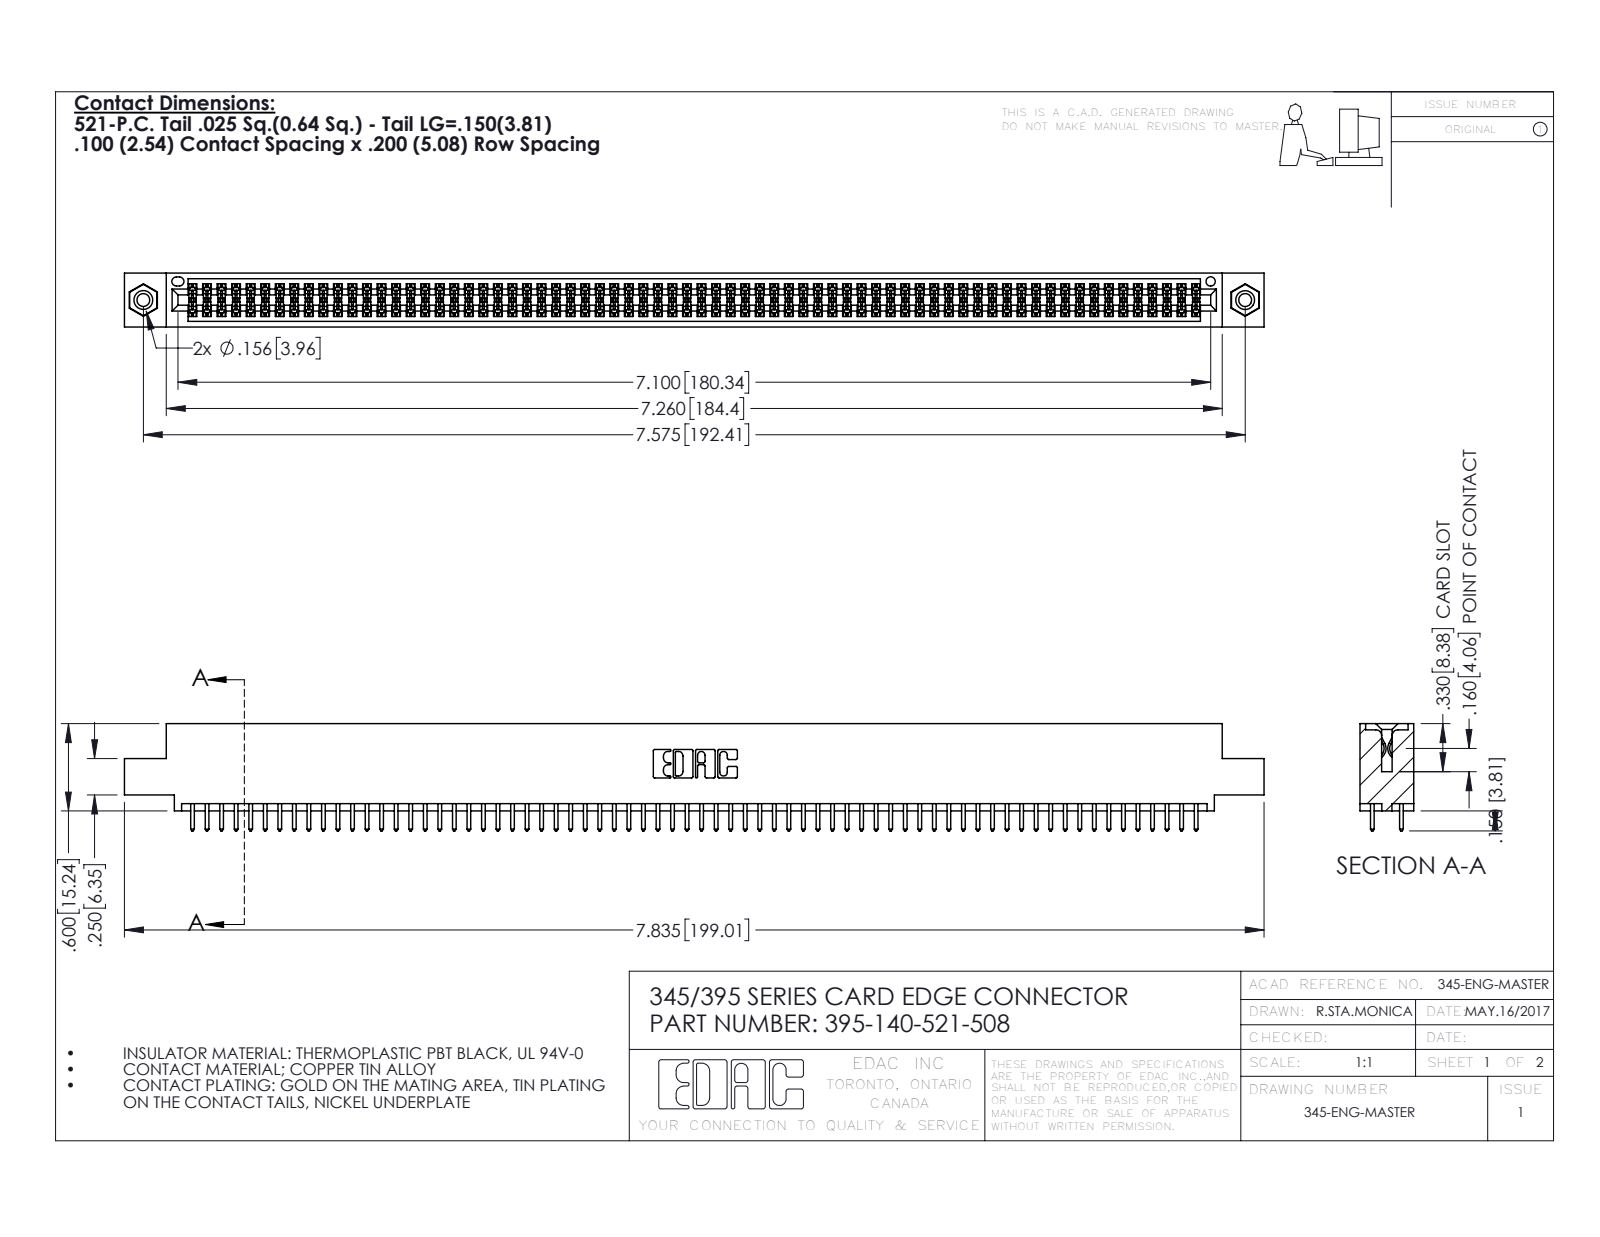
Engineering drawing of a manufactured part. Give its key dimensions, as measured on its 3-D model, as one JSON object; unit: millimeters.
{"part_name": "345 Part_0.110 Offset - 0.156 Dia-TI; 395-140-521-508; 345-250-001_345-250-003-102; 345-292-001_345-293-121", "step_written_by": "SolidWorks 2016 (CONFIG_CONTROL_DESIGN)", "units": "millimeters", "bodies": {"solids": 143, "faces": 7190, "planar": 4736, "cylindrical": 2438, "other": 16}, "overall_size": [199, 18.7, 9.4], "volume_mm3": 19450, "surface_area_mm2": 29030, "round_holes": [[2.3, 2], [3.2, 2], [4, 2], [1.6, 1]], "round_bosses_or_shafts": [[3.9, 2]], "partial_cylinders_radius": [[0.2, 210], [0.3, 140], [0.3, 22], [0.2, 6], [0.8, 6], [0.7, 3], [0.4, 2], [0.5, 2]], "face_to_face_distances": [1.8, 7.6, 5.1, 2.5, 6.9, 0.6, 9.4, 5.7, 4.4, 3.8], "hole_center_spacings": [6.9, 186.4, 192.4]}
